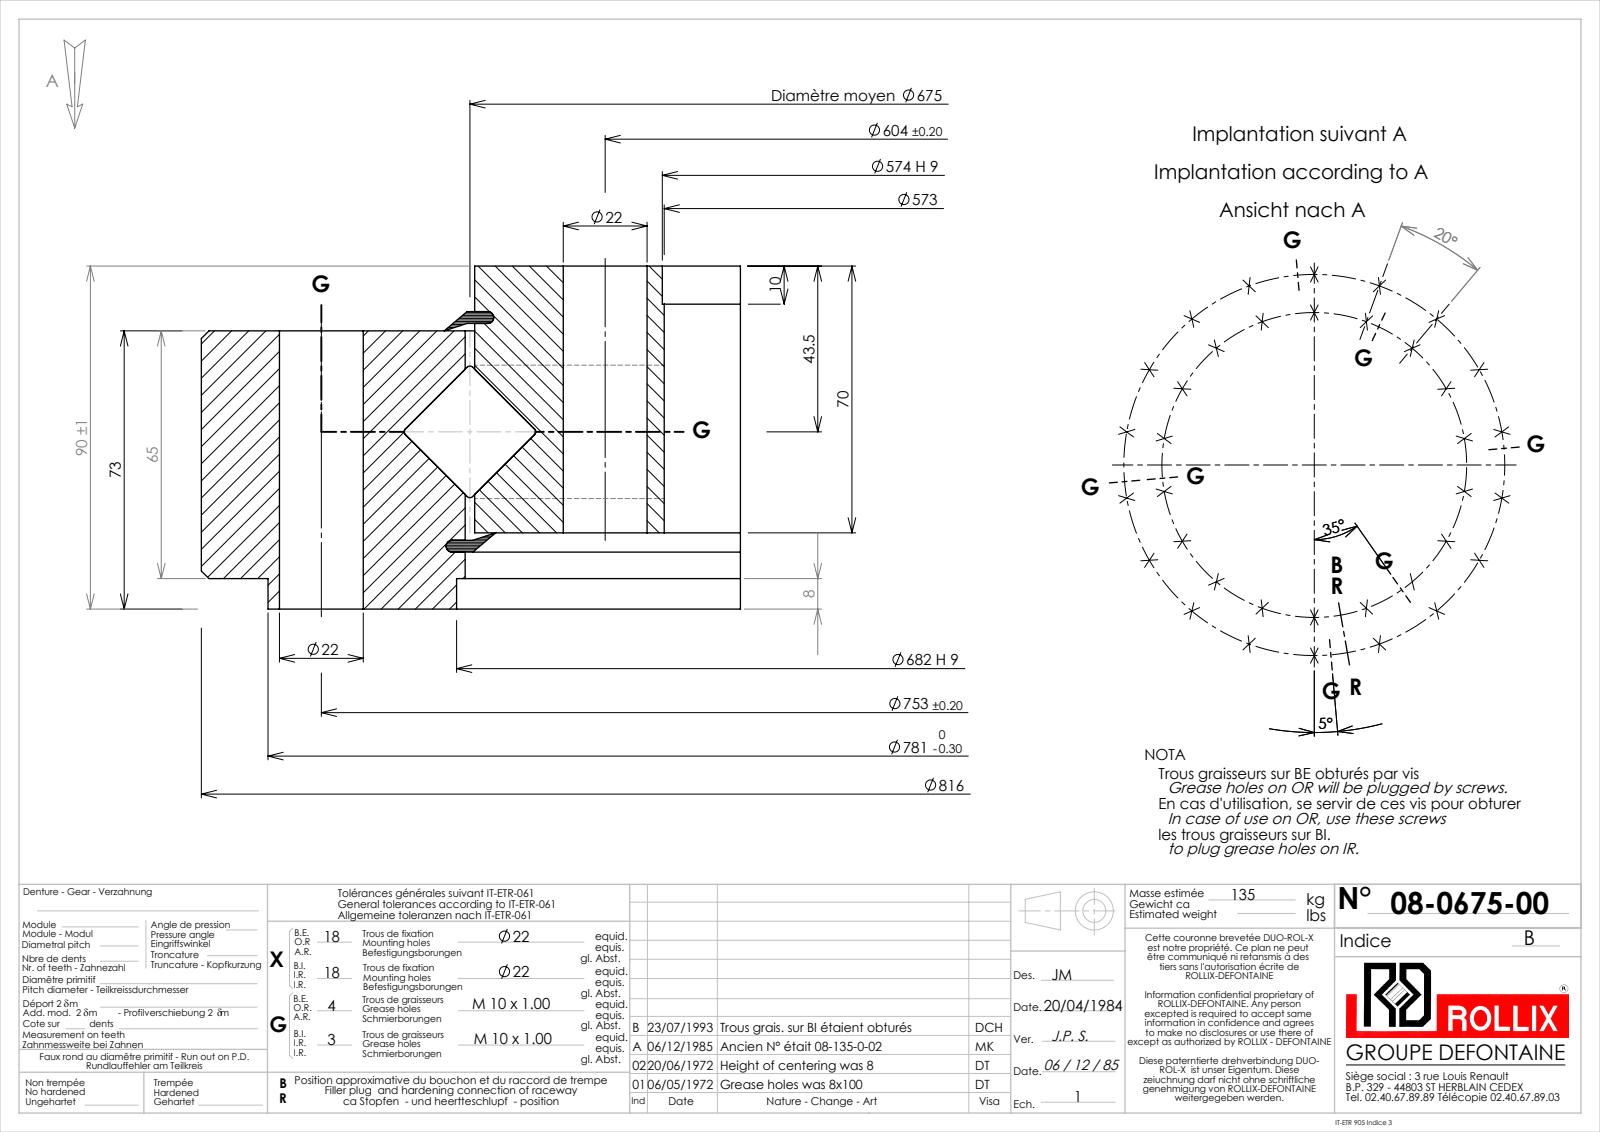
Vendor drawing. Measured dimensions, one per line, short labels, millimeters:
name: 08-0675-00
written by: SolidWorks 2016 (CONFIG_CONTROL_DESIGN)
unit: mm
bodies: 5 solids, 180 faces (17 planar, 110 cylindrical, 53 other)
size: 816 × 816 × 90
volume: 16 200 000 mm³; area: 1 511 000 mm²
holes: 36× ⌀22, 7× ⌀9, 1× ⌀573, 1× ⌀574, 1× ⌀677.5, 1× ⌀682
bosses: 1× ⌀816, 1× ⌀781, 1× ⌀672.5, 1× ⌀25
face distances: 73, 20, 53, 90, 70, 17, 8, 12, 65, 82
hole spacings: 376.5, 638.09, 242.39, 439.85, 588.78, 668.32, 302, 345.33
